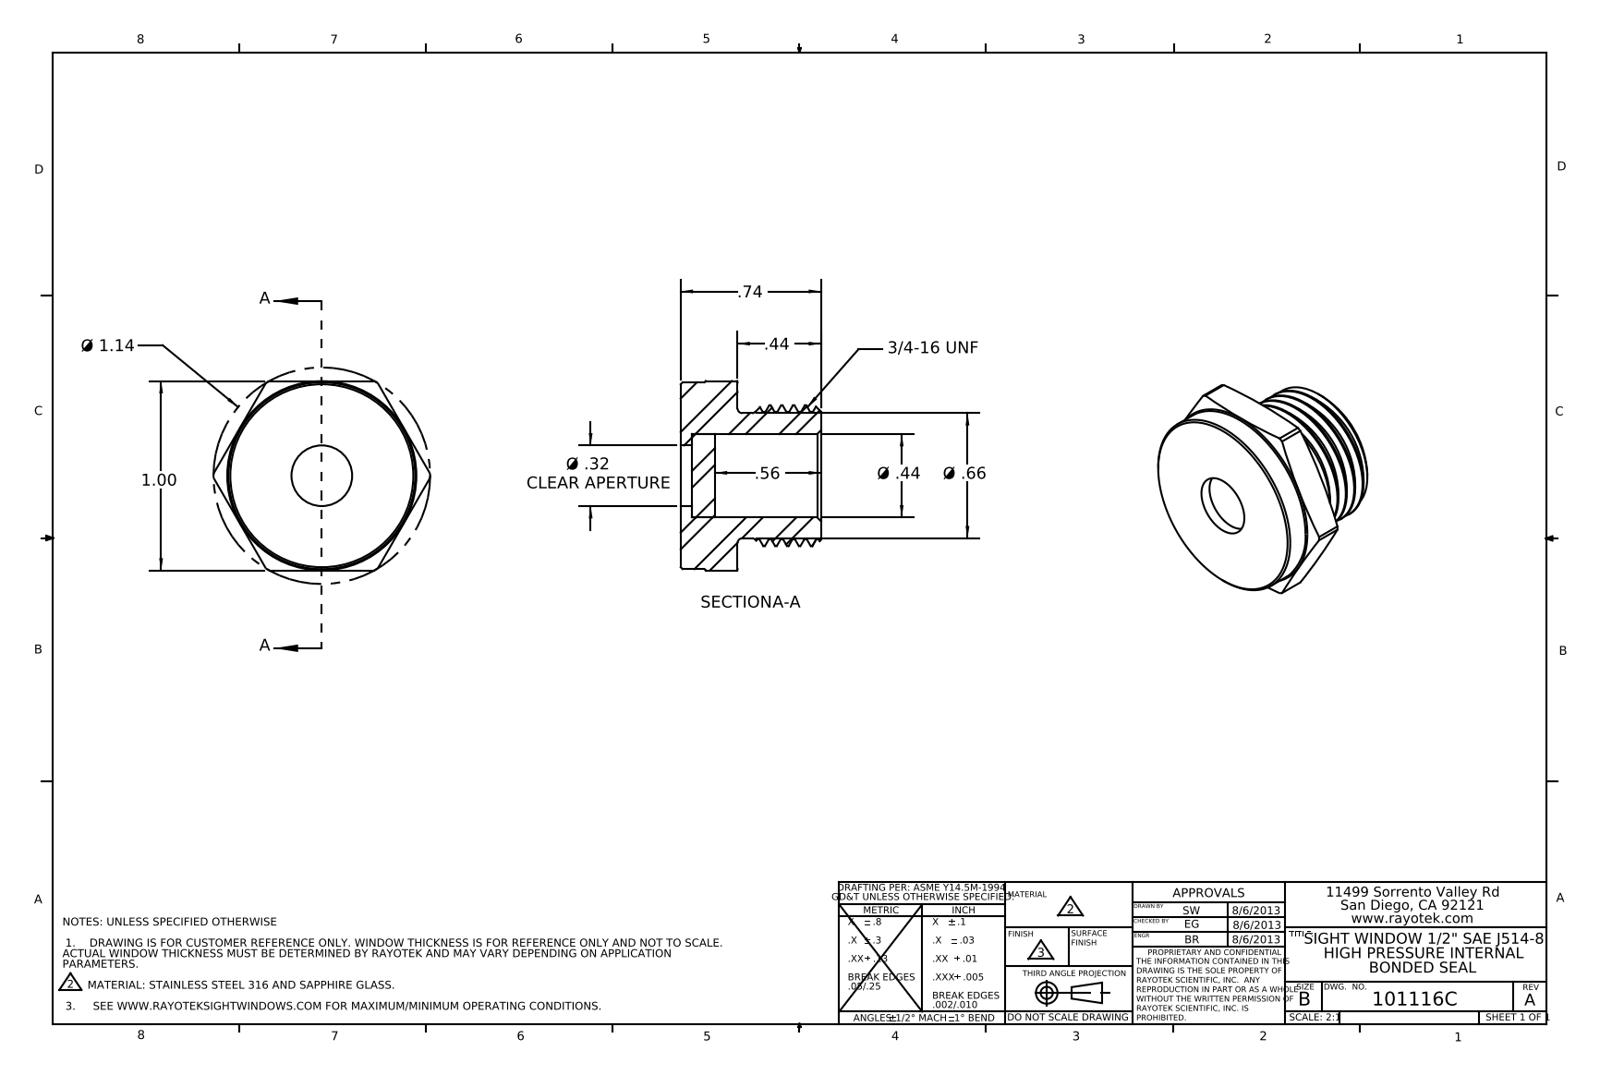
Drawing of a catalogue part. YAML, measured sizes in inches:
part_name: "403116"
step_written_by: "SolidWorks 2012 (AUTOMOTIVE_DESIGN)"
units: inches
bodies: {solids: 2, faces: 63, planar: 12, cylindrical: 28, other: 23}
overall_size: [1.143, 1, 0.74]
volume: 0.322
surface_area: 5.361
round_holes:
  - {diameter: 0.32, count: 1}
  - {diameter: 0.44, count: 1}
round_bosses_or_shafts:
  - {diameter: 0.985, count: 1}
  - {diameter: 0.743, count: 1}
  - {diameter: 0.66, count: 1}
partial_cylinders:
  - {radius: 0.571, count: 1}
face_to_face_distances: [0.3, 0.12, 1, 0.24, 0.06, 0.44, 0.68, 0.74, 0.56, 0.18]
